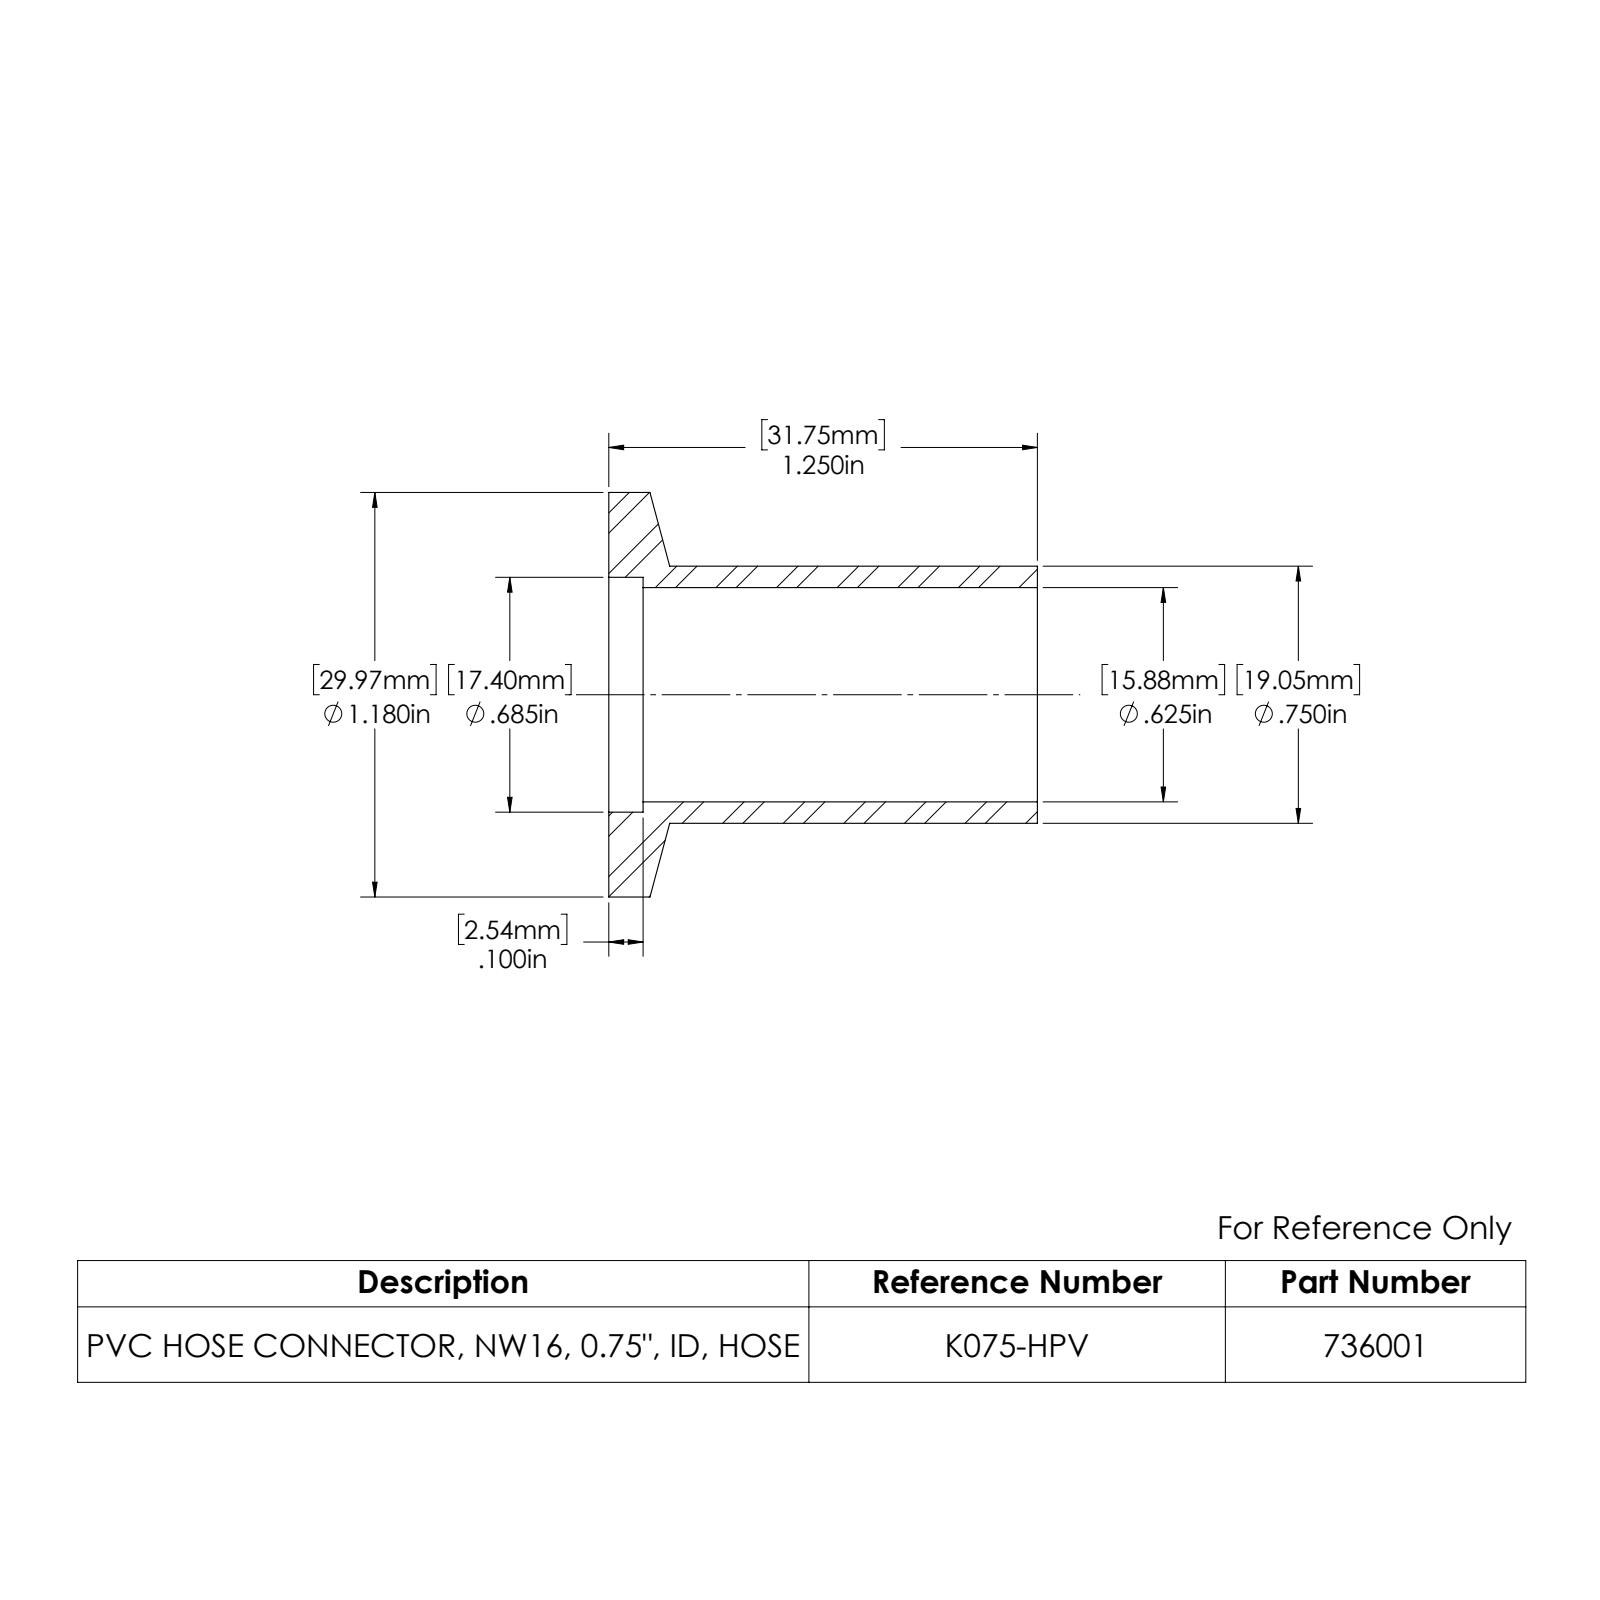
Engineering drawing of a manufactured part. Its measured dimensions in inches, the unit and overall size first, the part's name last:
Units: inches
Overall size (bounding box): 1.25 × 1.18 × 1.18
Round holes (diameter × count): ⌀0.625 ×1, ⌀0.685 ×1
Round bosses / shafts (diameter × count): ⌀1.18 ×1, ⌀0.75 ×1
Main face-to-face distances: 1.25, 1.15, 0.1
Volume: 0.258 in³ · Surface area: 7.041 in²
Bodies: 1 solid, 13 faces (3 planar, 8 cylindrical, 2 other)
Part name (STEP PRODUCT): 736001
STEP written by: SolidWorks 2022 (AUTOMOTIVE_DESIGN)
